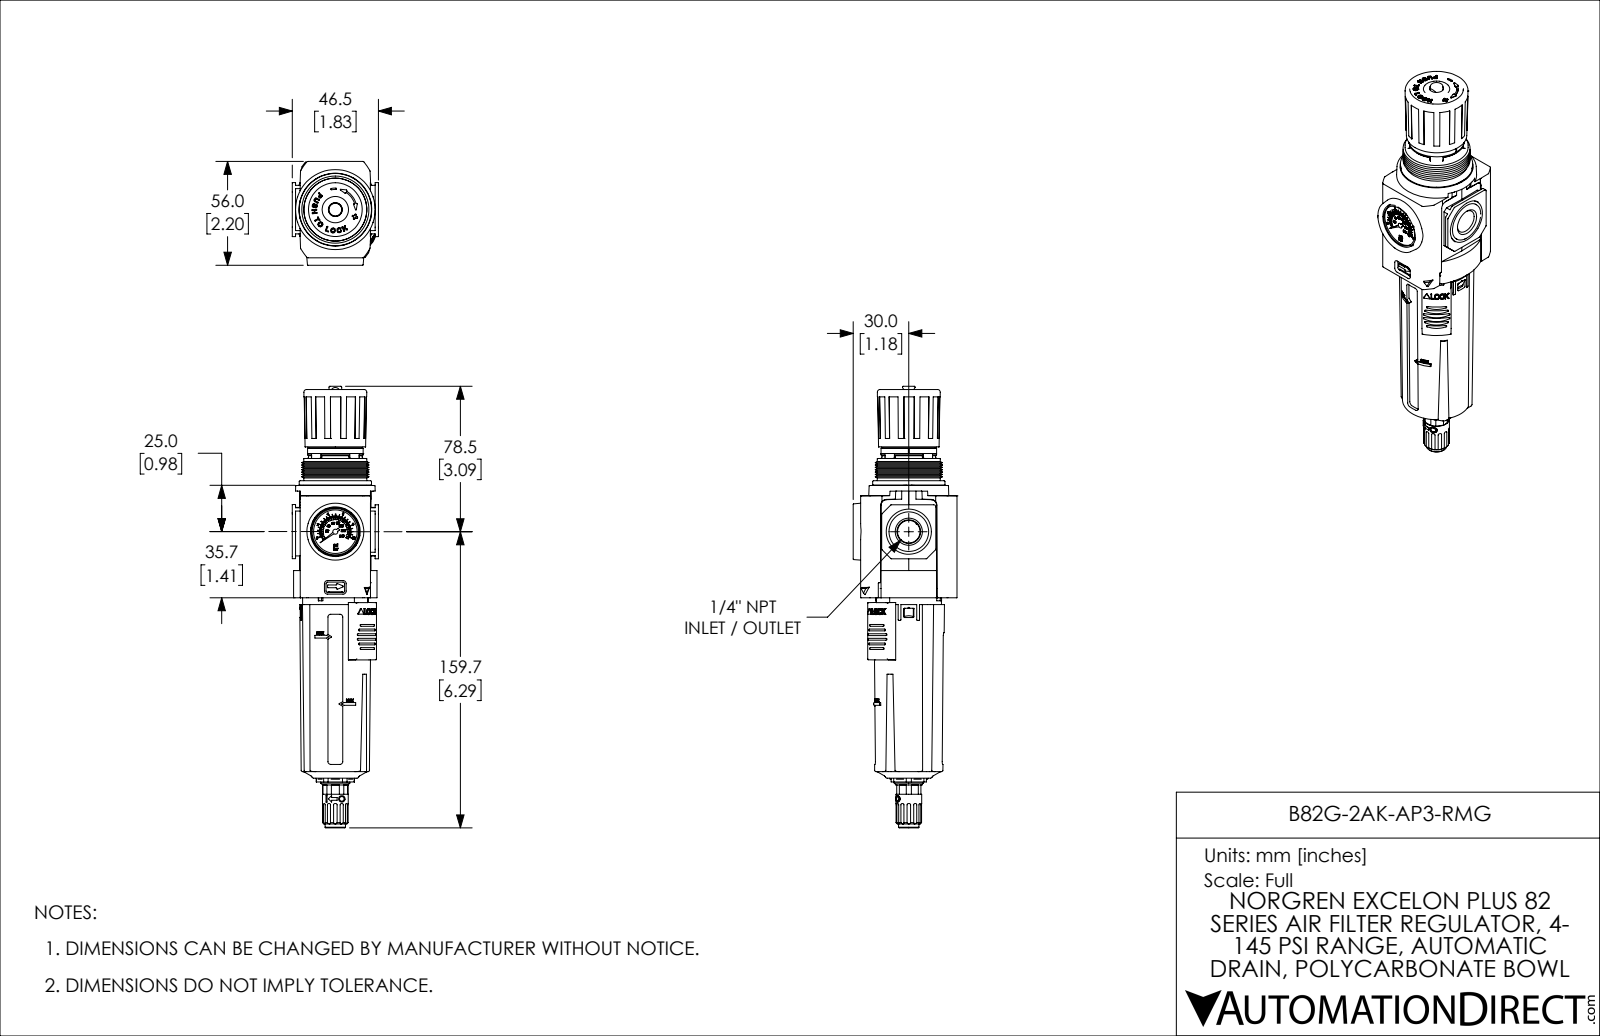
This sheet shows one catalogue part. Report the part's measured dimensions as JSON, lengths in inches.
{"part_name": "B82G-2AK-AP3-RMG", "step_written_by": "SolidWorks 2021 (CONFIG_CONTROL_DESIGN)", "units": "inches", "bodies": {"solids": 8, "faces": 2715, "planar": 1038, "cylindrical": 1255, "other": 422}, "overall_size": [9.379, 2.205, 1.831], "volume_in3": 17.46, "surface_area_in2": 113.6, "round_holes": [[0.097, 4], [0.138, 2], [0.098, 1], [0.128, 1], [0.197, 1], [0.236, 1], [0.259, 1], [0.63, 1], [0.925, 1], [1.102, 1], [1.354, 1]], "round_bosses_or_shafts": [[0.224, 2], [0.118, 2], [1.535, 1], [1.388, 1], [1.356, 1], [1.339, 1], [1.291, 1], [1.257, 1]], "partial_cylinders_radius": [[0.02, 55], [0.039, 42], [0.009, 25], [0.031, 20], [0.006, 19], [0.012, 15], [0.012, 12], [0.012, 12]], "face_to_face_distances": [0.059, 1.988, 1.693, 0.354, 1.634, 0.295, 1.417, 1.475, 0.182, 1.352], "hole_center_spacings": [0.63, 1.091, 1.26, 2.705, 3.325, 2.965, 5.374, 5.402]}
